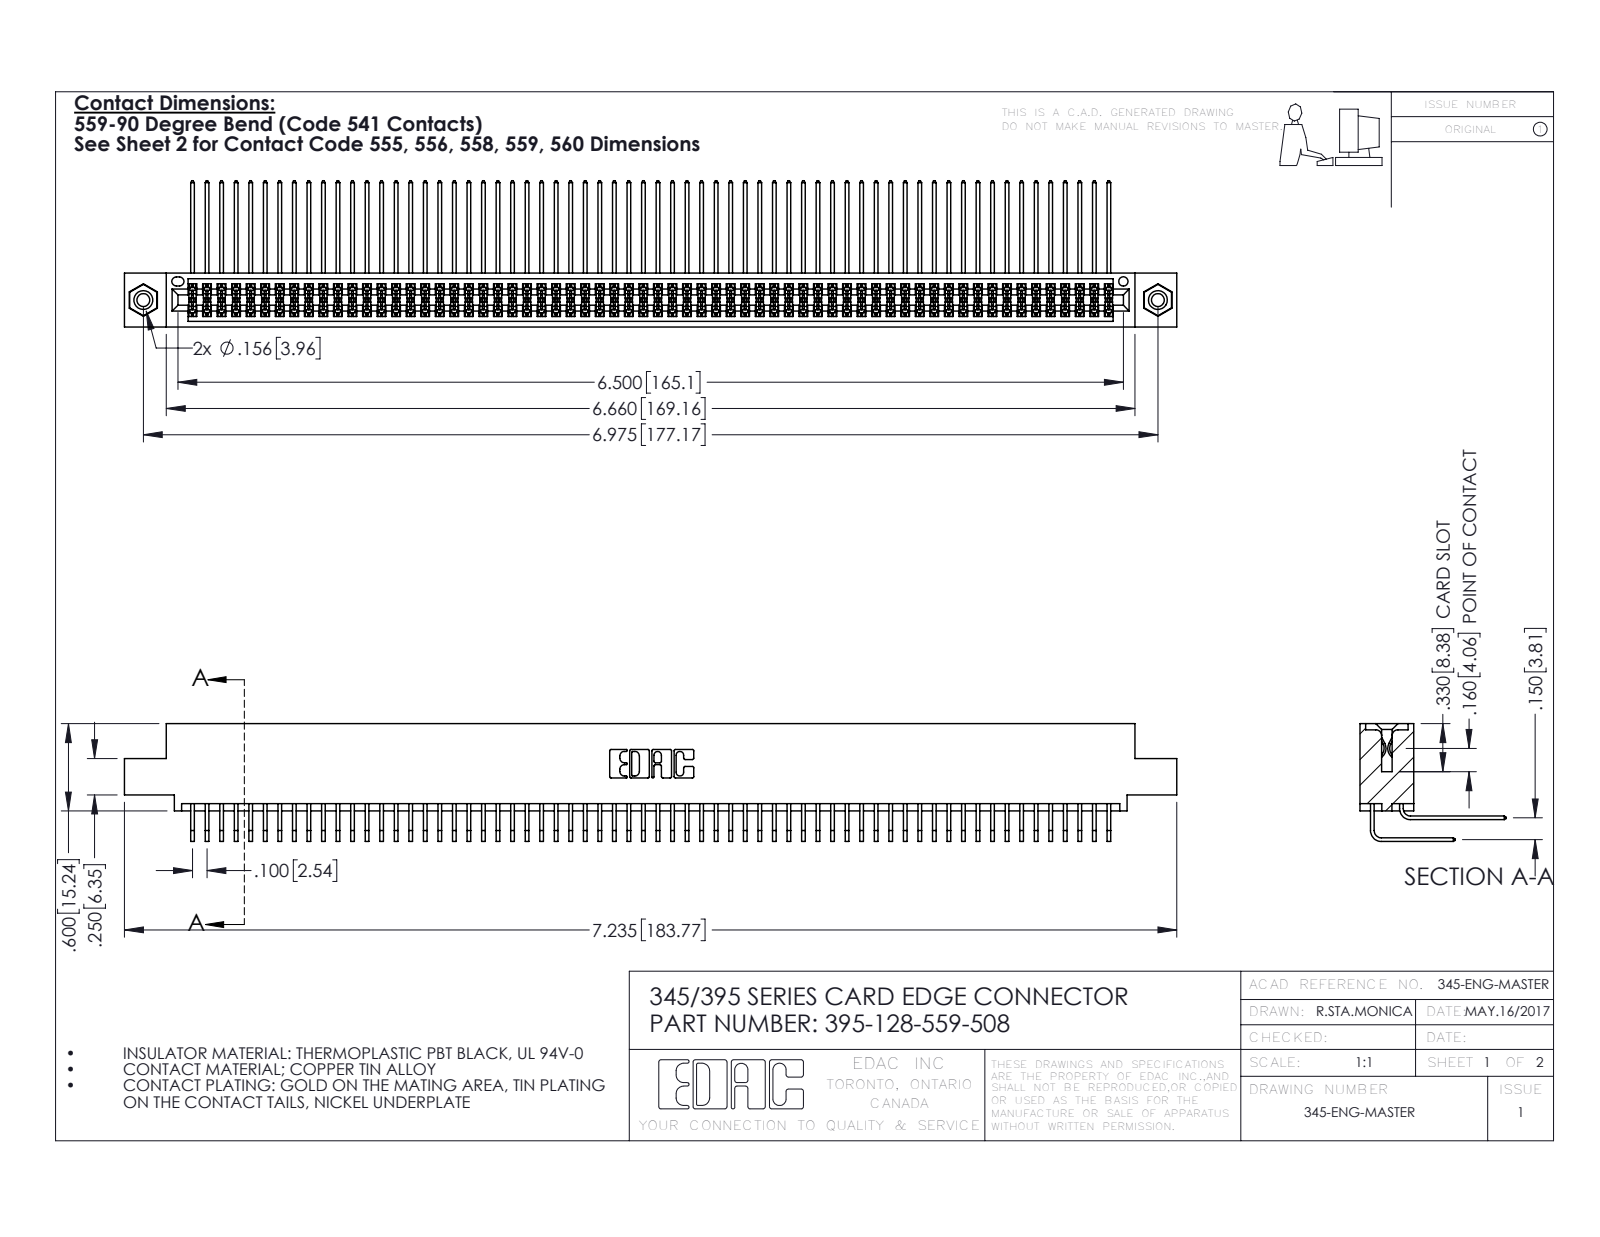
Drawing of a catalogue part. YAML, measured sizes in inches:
part_name: "345-292-001_558 559 Tail - 1; 345-250-001_345-250-003-102; 395-128-559-508; 345-292-001_559 Tail - 2 (+1 more)"
step_written_by: "SolidWorks 2016 (CONFIG_CONTROL_DESIGN)"
units: inches
bodies: {solids: 131, faces: 6846, planar: 4596, cylindrical: 2234, other: 16}
overall_size: [7.235, 1.005, 0.809]
volume: 1.142
surface_area: 49.08
round_holes:
  - {diameter: 0.089, count: 2}
  - {diameter: 0.125, count: 2}
  - {diameter: 0.156, count: 2}
  - {diameter: 0.064, count: 1}
round_bosses_or_shafts:
  - {diameter: 0.155, count: 2}
partial_cylinders:
  - {radius: 0.006, count: 193}
  - {radius: 0.01, count: 22}
  - {radius: 0.007, count: 6}
  - {radius: 0.031, count: 6}
  - {radius: 0.026, count: 3}
  - {radius: 0.014, count: 2}
  - {radius: 0.019, count: 2}
  - {radius: 0.022, count: 2}
face_to_face_distances: [0.072, 0.298, 0.2, 0.37, 0.098, 0.272, 0.025, 0.225, 0.175, 0.15]
hole_center_spacings: [0.27, 6.739, 6.975]
